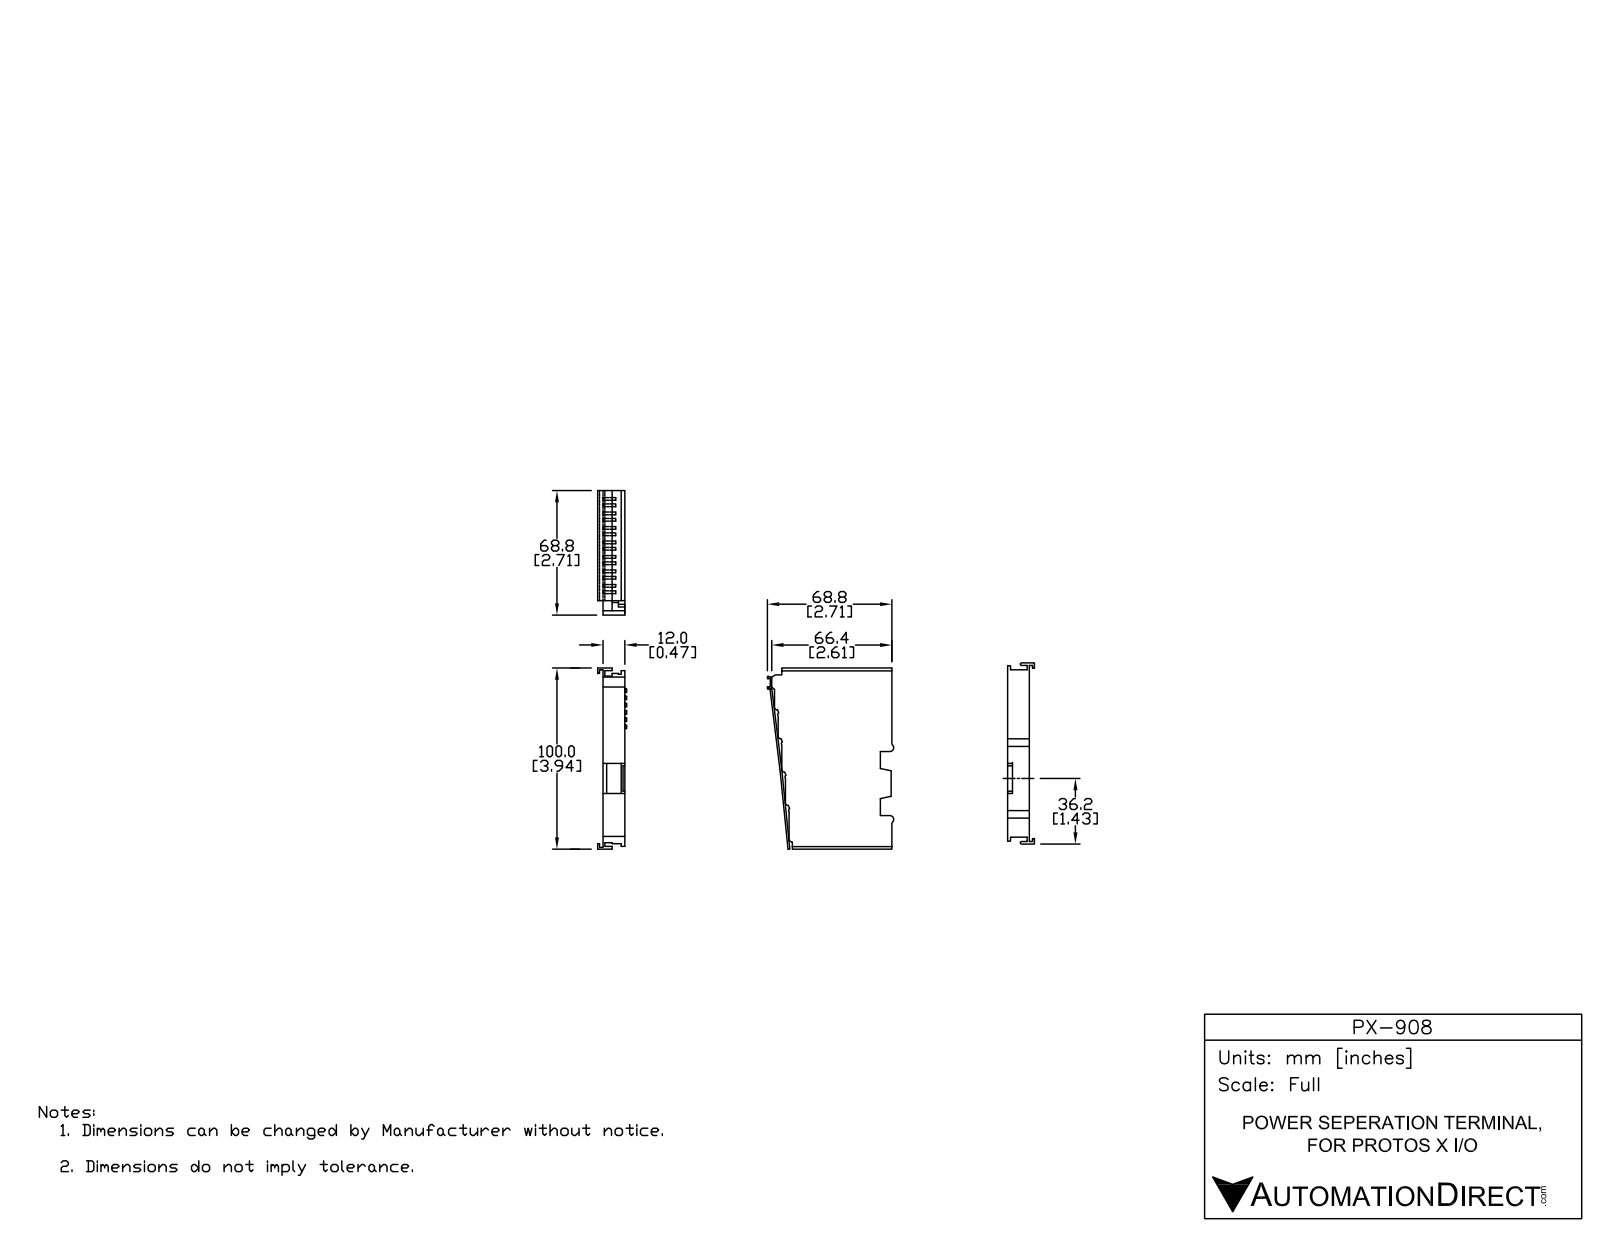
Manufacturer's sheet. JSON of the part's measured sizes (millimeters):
{"part_name": "PX-908", "step_written_by": "SolidWorks 2014 (AUTOMOTIVE_DESIGN)", "units": "millimeters", "bodies": {"solids": 21, "faces": 1329, "planar": 948, "cylindrical": 321, "other": 60}, "overall_size": [100.25, 71.26, 15.15], "volume_mm3": 60632, "surface_area_mm2": 35844, "round_holes": [[4, 8], [3.5, 4]], "partial_cylinders_radius": [[0.3, 46], [0.25, 36], [0.38, 12], [0.12, 10], [1, 9], [0.17, 4], [1.03, 4], [1.38, 4]], "face_to_face_distances": [12, 1, 10, 2, 1.85, 8.7, 11, 3.15, 1.22, 1.3], "hole_center_spacings": [4.5, 5, 18.4, 19.07, 6.36, 16, 16.76, 20.41]}
